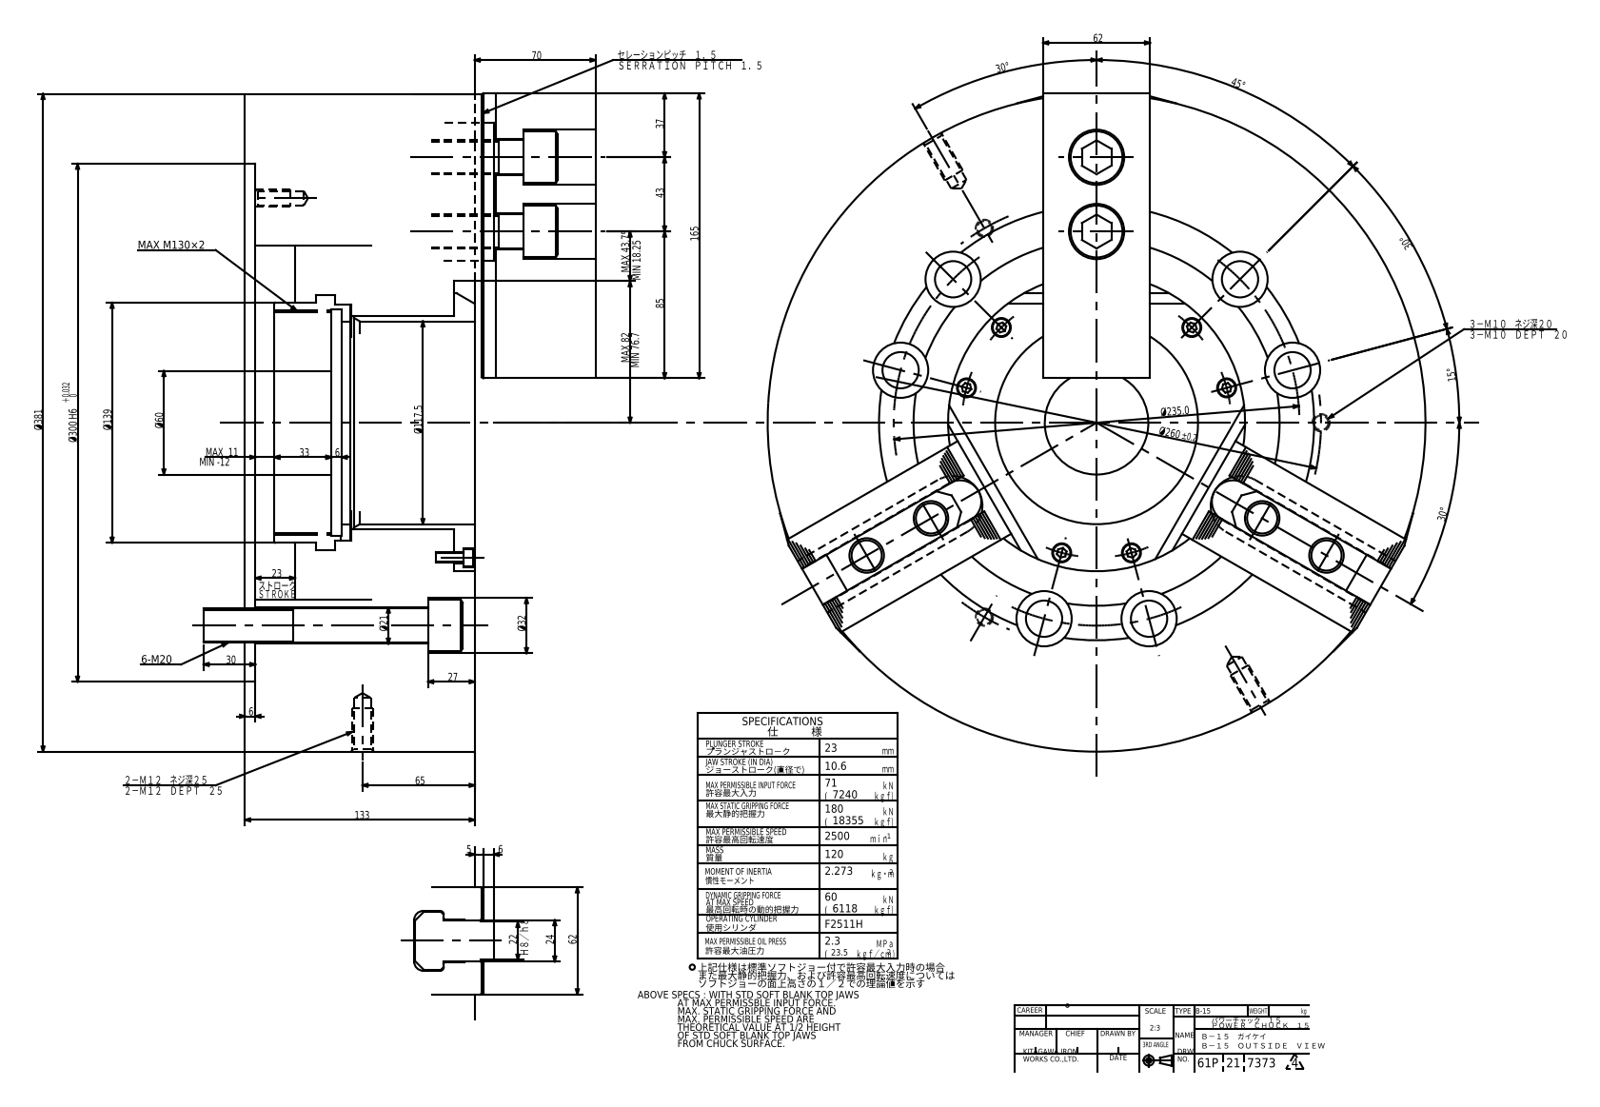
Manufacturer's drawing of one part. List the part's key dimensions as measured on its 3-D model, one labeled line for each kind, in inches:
STEP written by: ST-DEVELOPER v16.7 (AUTOMOTIVE_DESIGN)
Units: inches
Bodies: 1 solid, 5125 faces (4412 planar, 318 cylindrical, 395 other)
Overall size (bounding box): 15.6 × 15.227 × 8.945
Volume: 884.8 in³ · Surface area: 1 700 in²
Round holes (diameter × count): ⌀0.433 ×12, ⌀0.827 ×12, ⌀1.26 ×12, ⌀0.197 ×10, ⌀0.236 ×10, ⌀0.33 ×9, ⌀0.394 ×9, ⌀0.194 ×6, ⌀0.26 ×6, ⌀0.669 ×6, ⌀0.787 ×6, ⌀0.059 ×3
Round bosses / shafts (diameter × count): ⌀1.181 ×12, ⌀0.787 ×6, ⌀0.63 ×6, ⌀0.394 ×6, ⌀15 ×1, ⌀7.469 ×1, ⌀5.827 ×1, ⌀5.394 ×1
Partial cylindrical surfaces — rounded edges, fillets, slot ends (radius × count): R0.016 ×12, R0.018 ×12, R0.031 ×12, R0.02 ×6, R0.039 ×6, R0.071 ×6, R0.122 ×6, R0.197 ×6
Main face-to-face distances: 5.236, 0.236, 5, 2.441, 0.906, 8, 7.764, 2.764, 0.472, 1.732
Hole centre spacings: 3.327, 6.711, 0.873, 2.495, 2.655, 3.272, 4.114, 4.498
